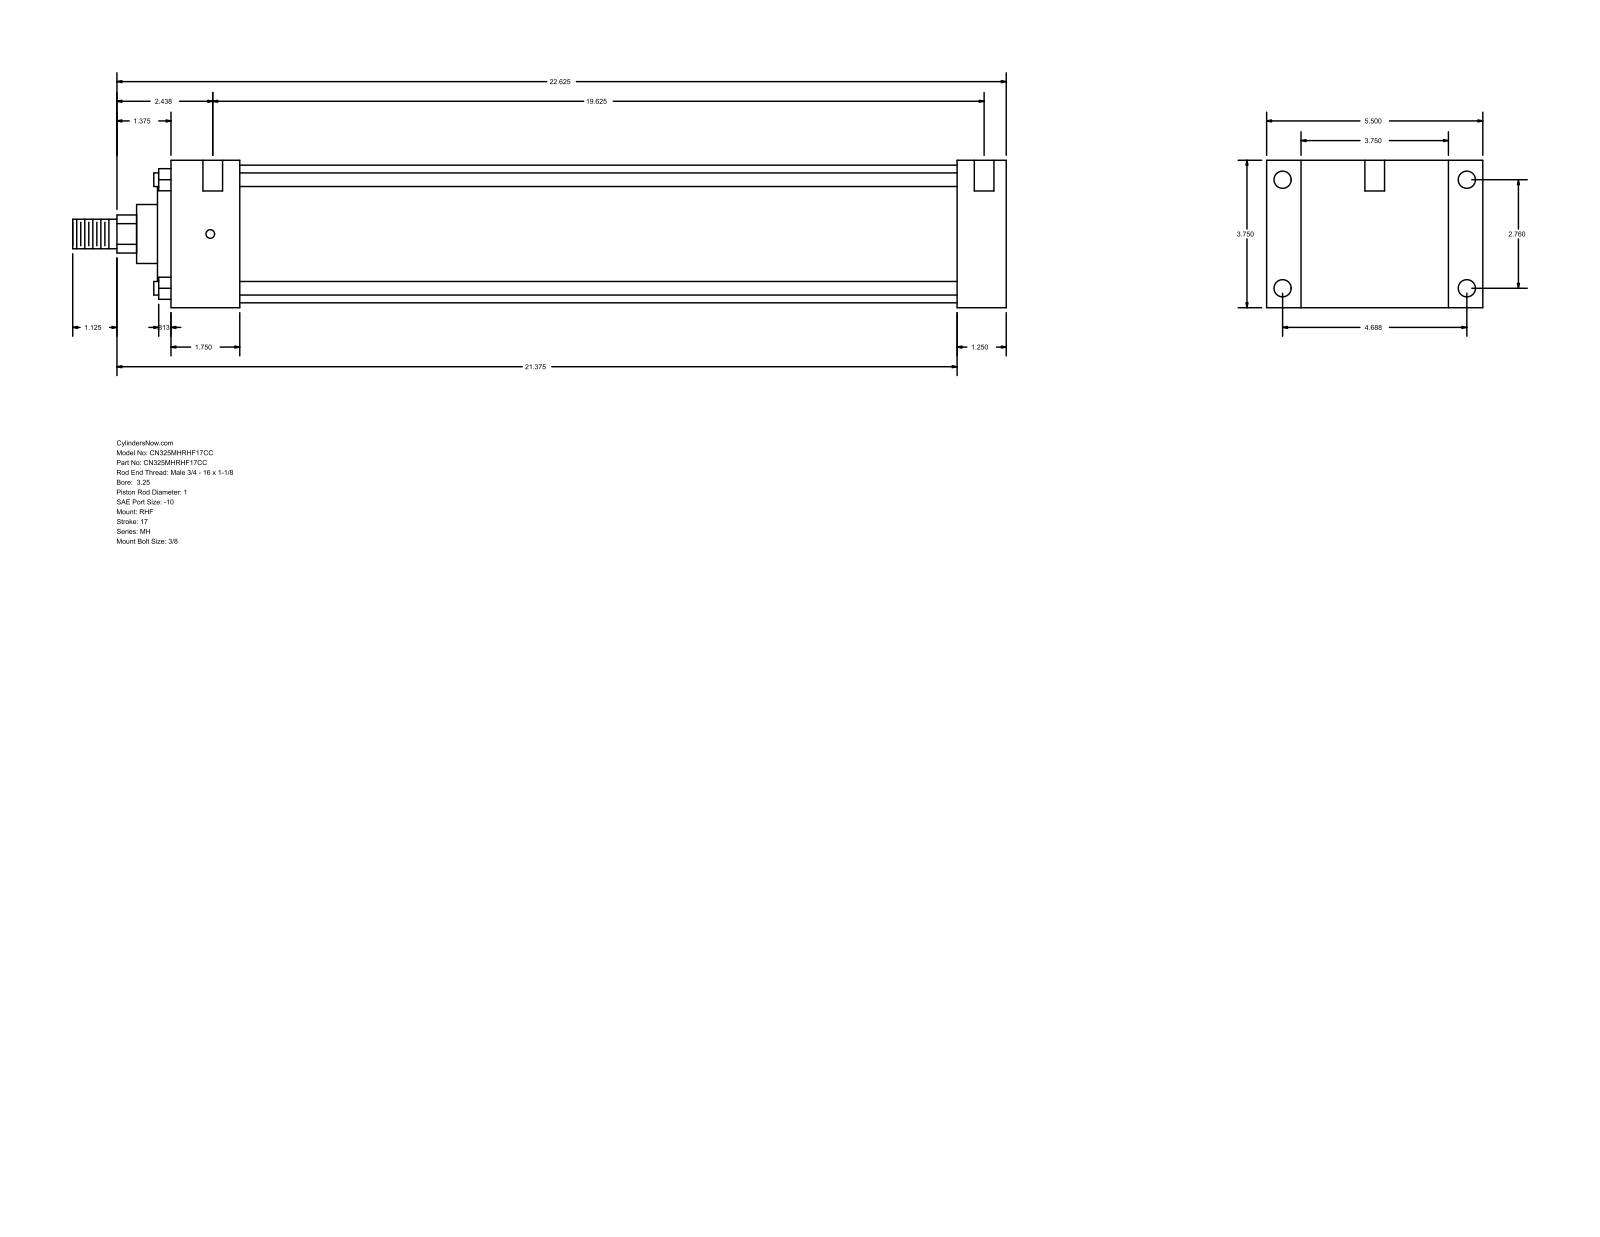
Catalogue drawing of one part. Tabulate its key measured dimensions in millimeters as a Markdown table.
| quantity | value |
| --- | --- |
| part name | MH_RHF__0325_1 |
| STEP written by | GSSL Pune (CONFIG_CONTROL_DESIGN) |
| units | millimeters |
| bodies | 0 solids, 90 faces (61 planar, 29 cylindrical, 0 other) |
| overall size | 603.25 × 139.7 × 95.25 |
| round holes (diameter × count) | 5.56 × 4, 11.13 × 4, 12.7 × 2 |
| round bosses / shafts (diameter × count) | 8.76 × 4, 88.9 × 1, 60.33 × 1, 38.1 × 1, 25.4 × 1, 19.05 × 1 |
| partial cylindrical surfaces (radius × count) | 12.29 × 1 |
| main face-to-face distances | 95.24, 31.75, 22.23, 117.47, 508, 539.75, 139.7, 44.46, 463.54, 495.29 |
| hole center spacings | 70.1, 119.06, 138.16, 504.82, 1.58, 4.76, 498.48, 500.06 |
